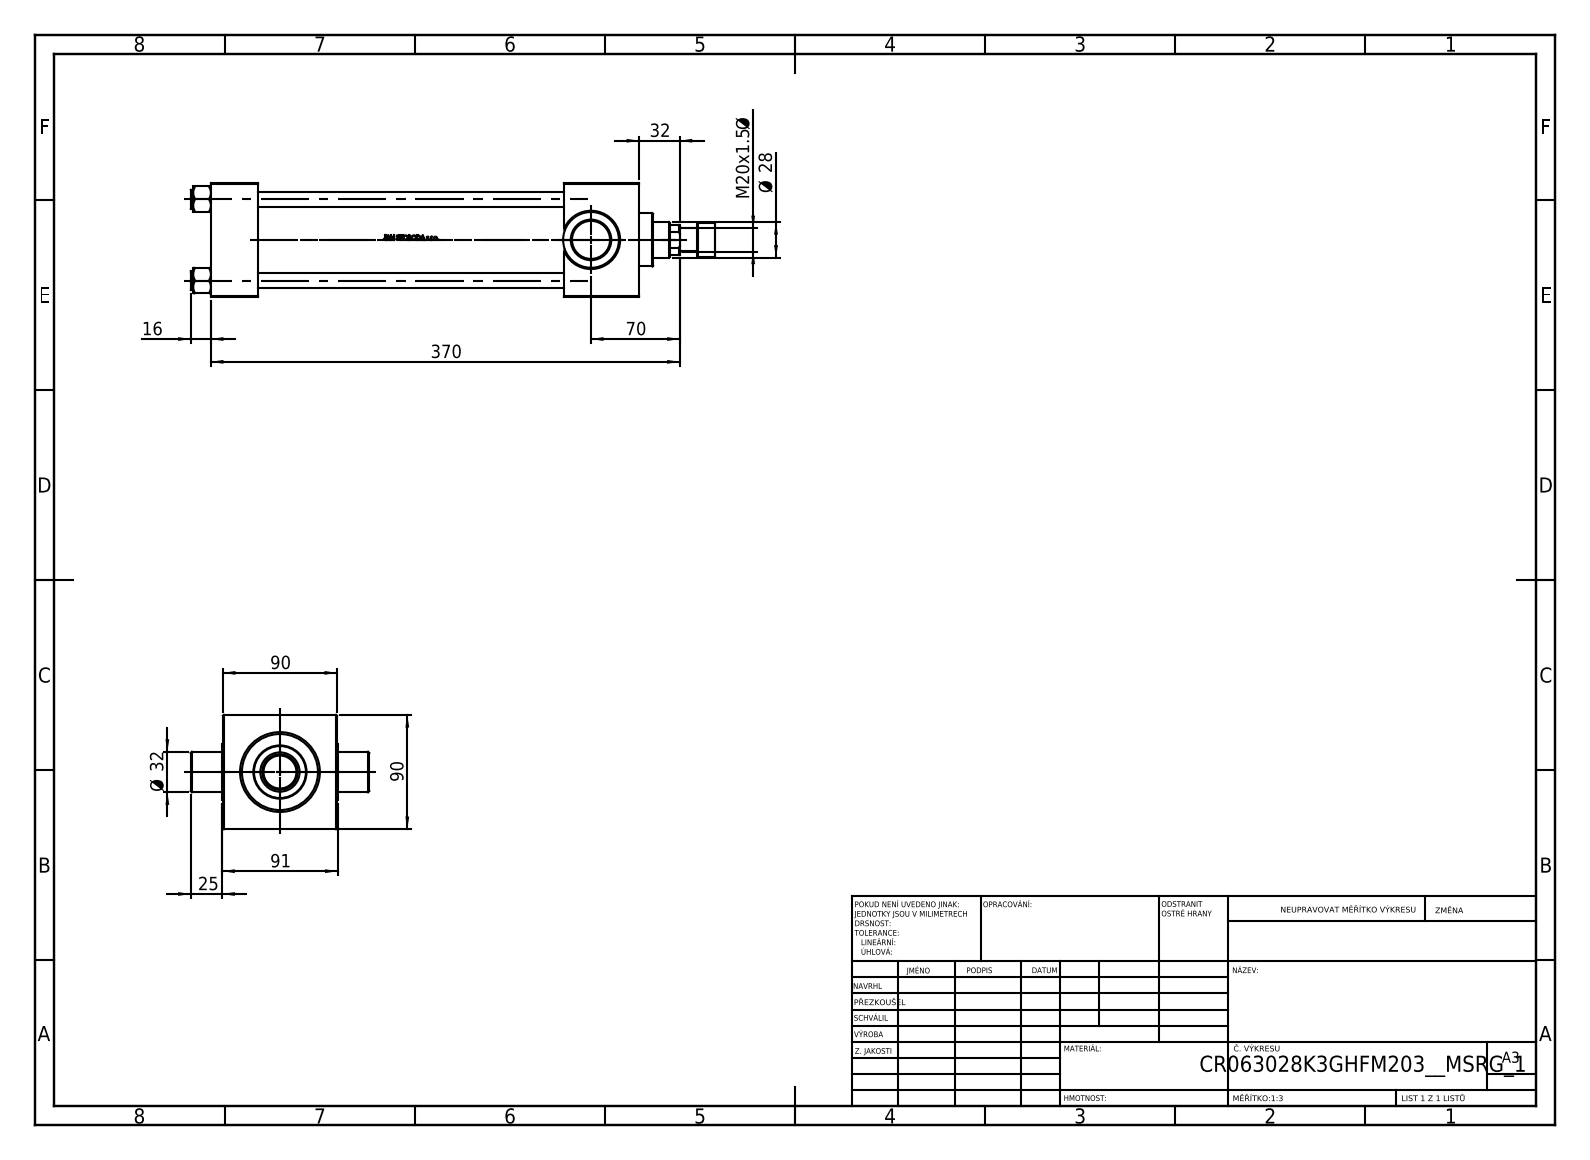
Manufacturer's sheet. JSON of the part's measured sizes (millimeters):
{"part_name": "NUT_M5_K; V215_VC_A; V215CR_ROD_END_F; V215CR_VCP_K (+2 more)", "step_written_by": "SolidWorks 2019 (CONFIG_CONTROL_DESIGN)", "units": "millimeters", "bodies": {"solids": 12, "faces": 1079, "planar": 433, "cylindrical": 116, "other": 530}, "overall_size": [414, 141, 90], "volume_mm3": 1325000, "surface_area_mm2": 299648, "round_holes": [[12, 4], [7, 1], [18.5, 1], [28, 1], [31, 1], [50, 1], [60, 1], [63, 1]], "round_bosses_or_shafts": [[15, 4], [69, 1], [42, 1], [32, 1], [27, 1], [18, 1]], "partial_cylinders_radius": [[22, 1]], "face_to_face_distances": [90, 37, 0.5, 89.5, 338, 301, 242, 279, 59, 89], "hole_center_spacings": [45.47, 64.3, 90.93]}
